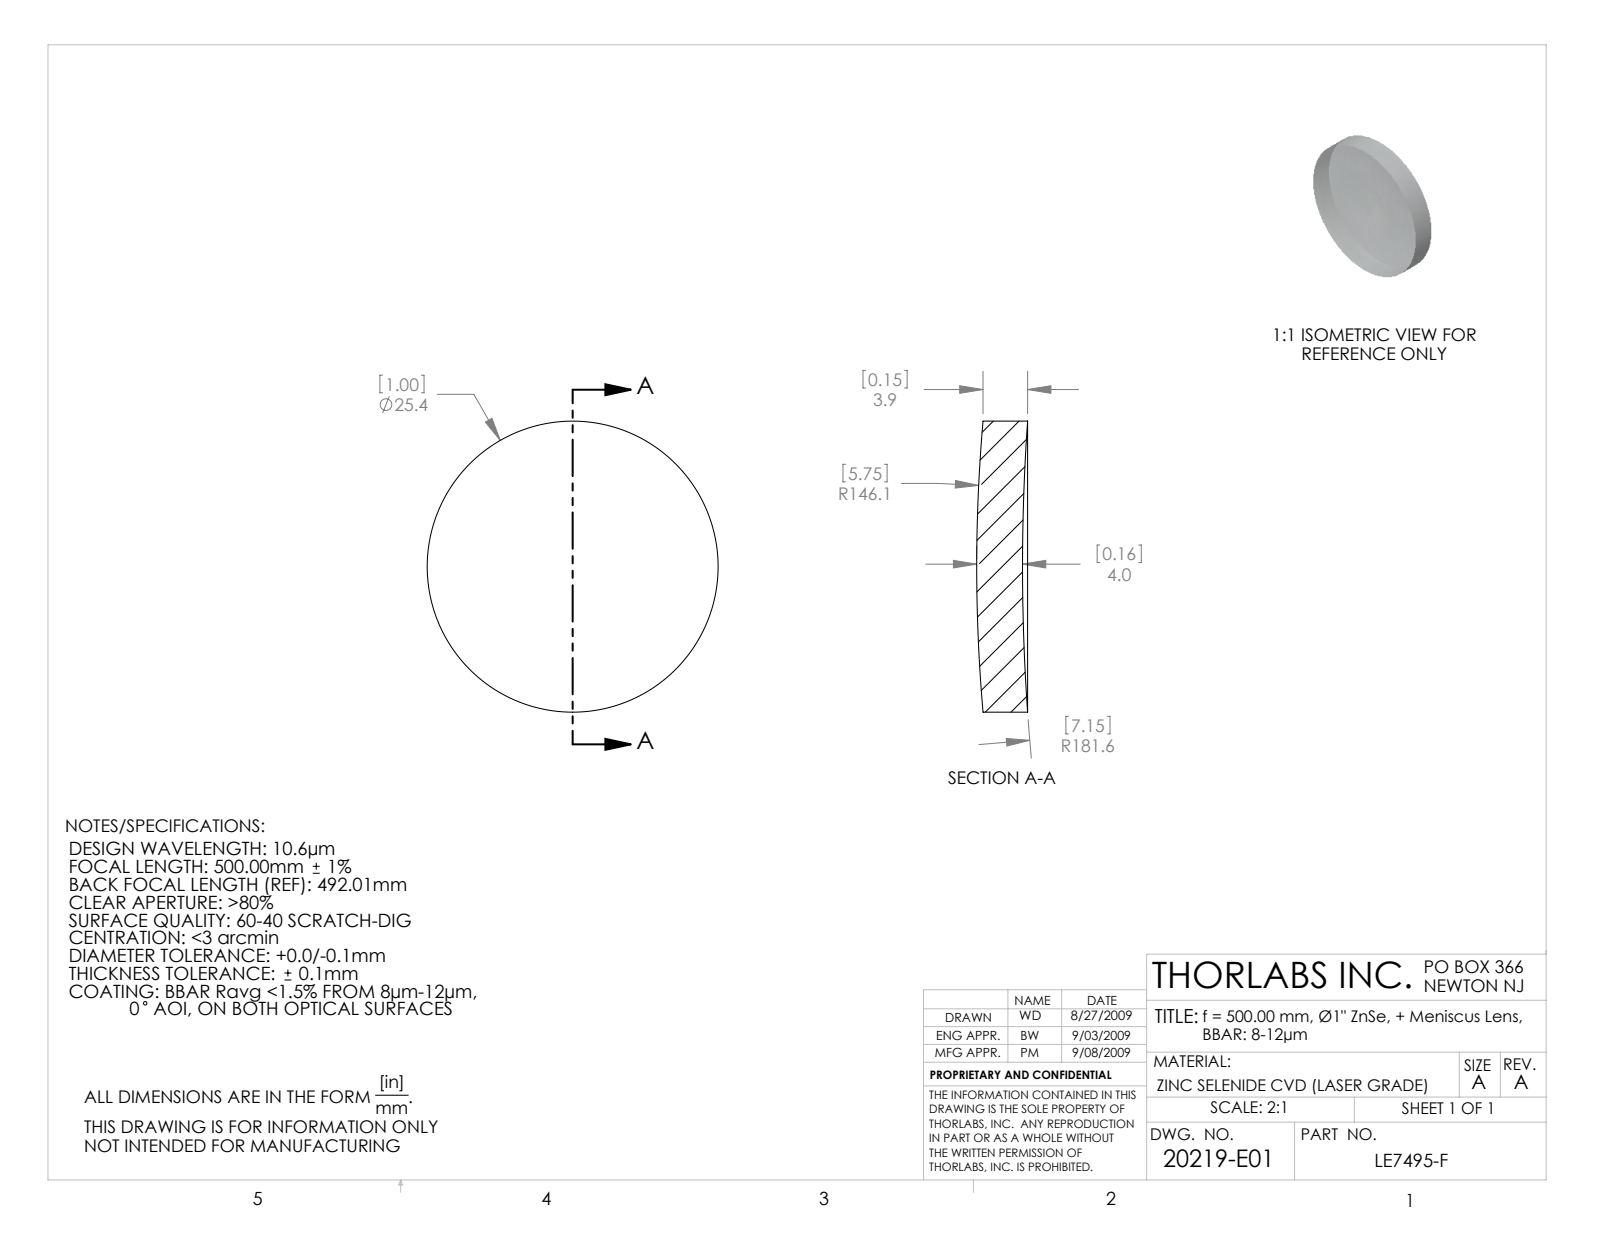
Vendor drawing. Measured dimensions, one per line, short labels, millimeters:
name: 20219-E0W
written by: SolidWorks 2007 (CONFIG_CONTROL_DESIGN)
unit: mm
bodies: 1 solid, 6 faces (0 planar, 2 cylindrical, 4 other)
size: 25.4 × 25.4 × 4.45
volume: 1 999 mm³; area: 1 326 mm²
bosses: 1× ⌀25.4
